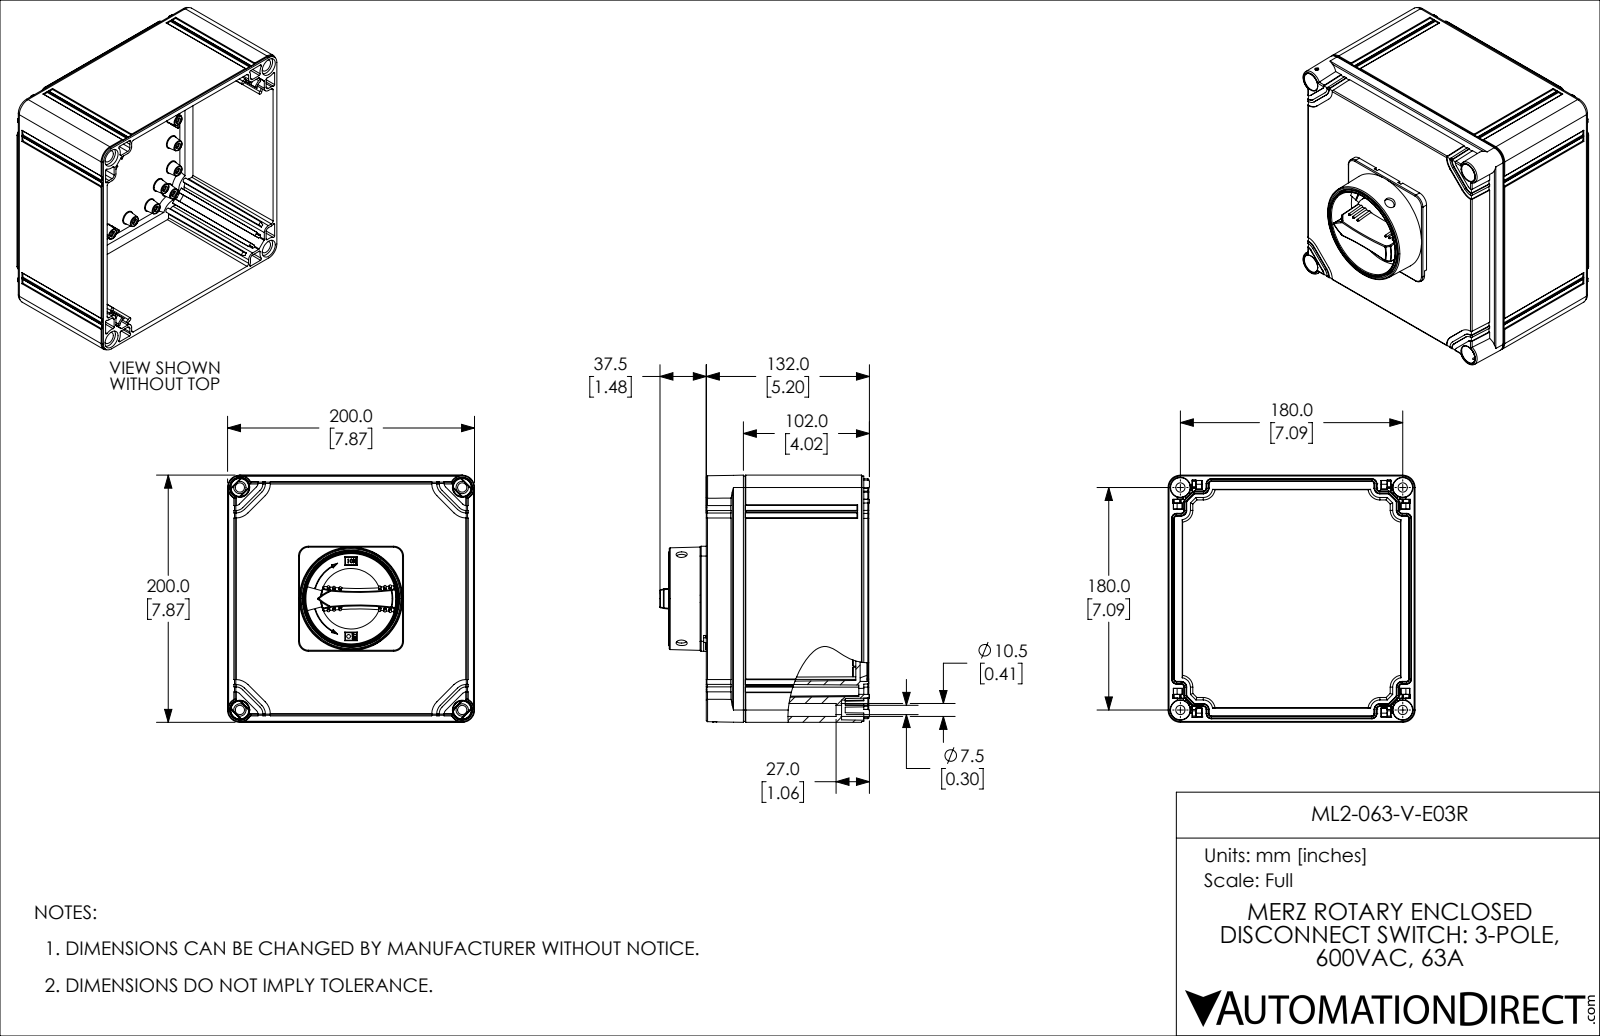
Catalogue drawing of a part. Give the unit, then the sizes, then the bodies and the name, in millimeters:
Units: millimetres
Overall size (bounding box): 200 × 200 × 169.5
Round holes (diameter × count): ⌀4.2 ×28, ⌀5 ×28, ⌀7.5 ×4, ⌀10 ×4, ⌀10.5 ×4, ⌀2.2 ×2, ⌀4 ×2, ⌀9 ×2, ⌀20.5 ×1, ⌀45 ×1, ⌀73.1 ×1
Round bosses / shafts (diameter × count): ⌀8 ×2, ⌀77 ×1, ⌀76.5 ×1, ⌀49 ×1, ⌀47.5 ×1, ⌀8.2 ×1, ⌀3.8 ×1, ⌀3 ×1
Partial cylindrical surfaces — rounded edges, fillets, slot ends (radius × count): R0.5 ×60, R0.2 ×16, R1 ×16, R1.7 ×16, R0.3 ×14, R8 ×13, R10 ×12, R4 ×8
Main face-to-face distances: 130, 3.5, 32.5, 97.5, 200, 94, 126.5, 5.5, 2.5, 133.5
Hole centre spacings: 25, 152.1, 150, 18, 20.6, 38.1, 42.7, 45.3
Volume: 1 860 000 mm³ · Surface area: 489 200 mm²
Bodies: 3 solids, 2645 faces (1335 planar, 484 cylindrical, 826 other)
Part name (STEP PRODUCT): ML2-063-V-E03R
STEP written by: SolidWorks 2019 (AUTOMOTIVE_DESIGN)
